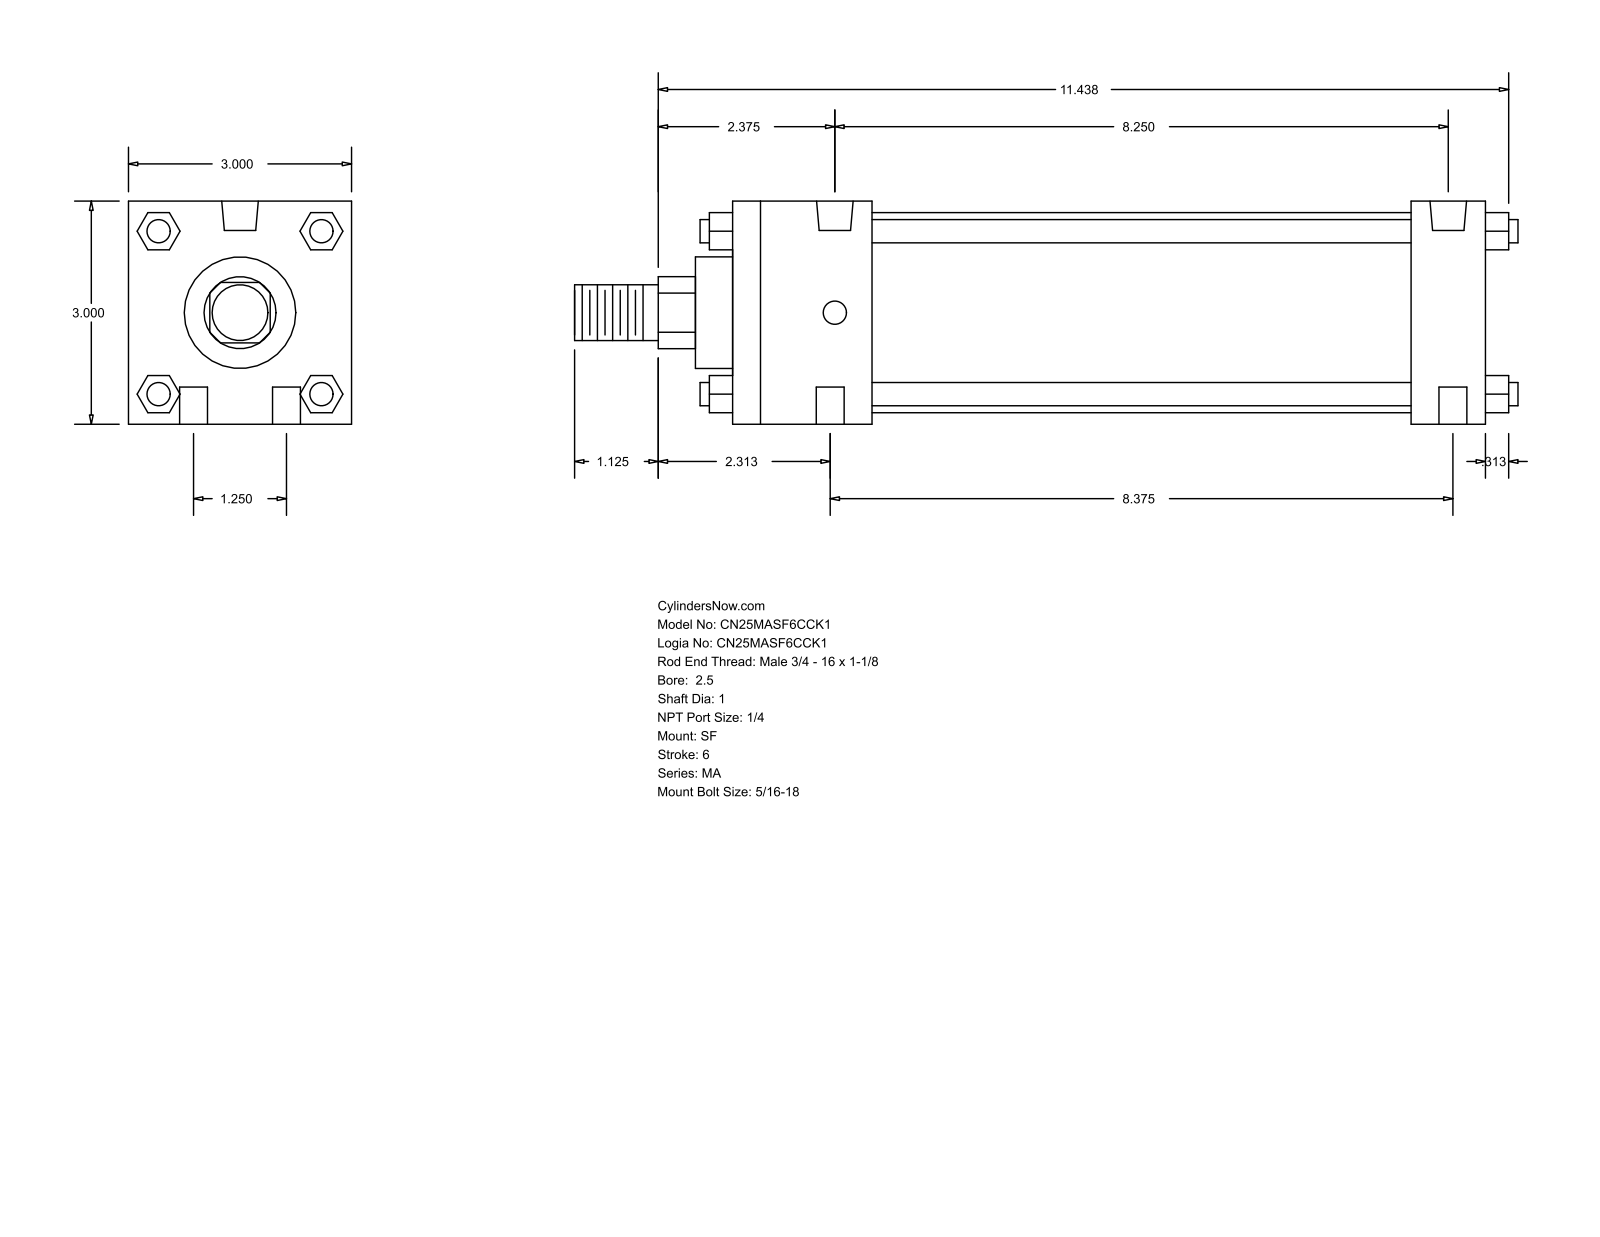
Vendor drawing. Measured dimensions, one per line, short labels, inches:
name: MA_SF__0250_1
written by: GSSL Pune (CONFIG_CONTROL_DESIGN)
unit: in
bodies: 0 solids, 124 faces (94 planar, 30 cylindrical, 0 other)
size: 12.687 × 3 × 3
holes: 4× ⌀0.375, 2× ⌀0.313, 2× ⌀0.492
bosses: 4× ⌀0.313, 1× ⌀2.69, 1× ⌀1.5, 1× ⌀1, 1× ⌀0.75
rounds: 1× R0.484
face distances: 3, 10.125, 0.5, 9.125, 1, 1.875, 7.25, 8.25, 1.095, 1.896
hole spacings: 0.628, 1.25, 8.25, 8.336, 8.336, 8.375, 8.468
